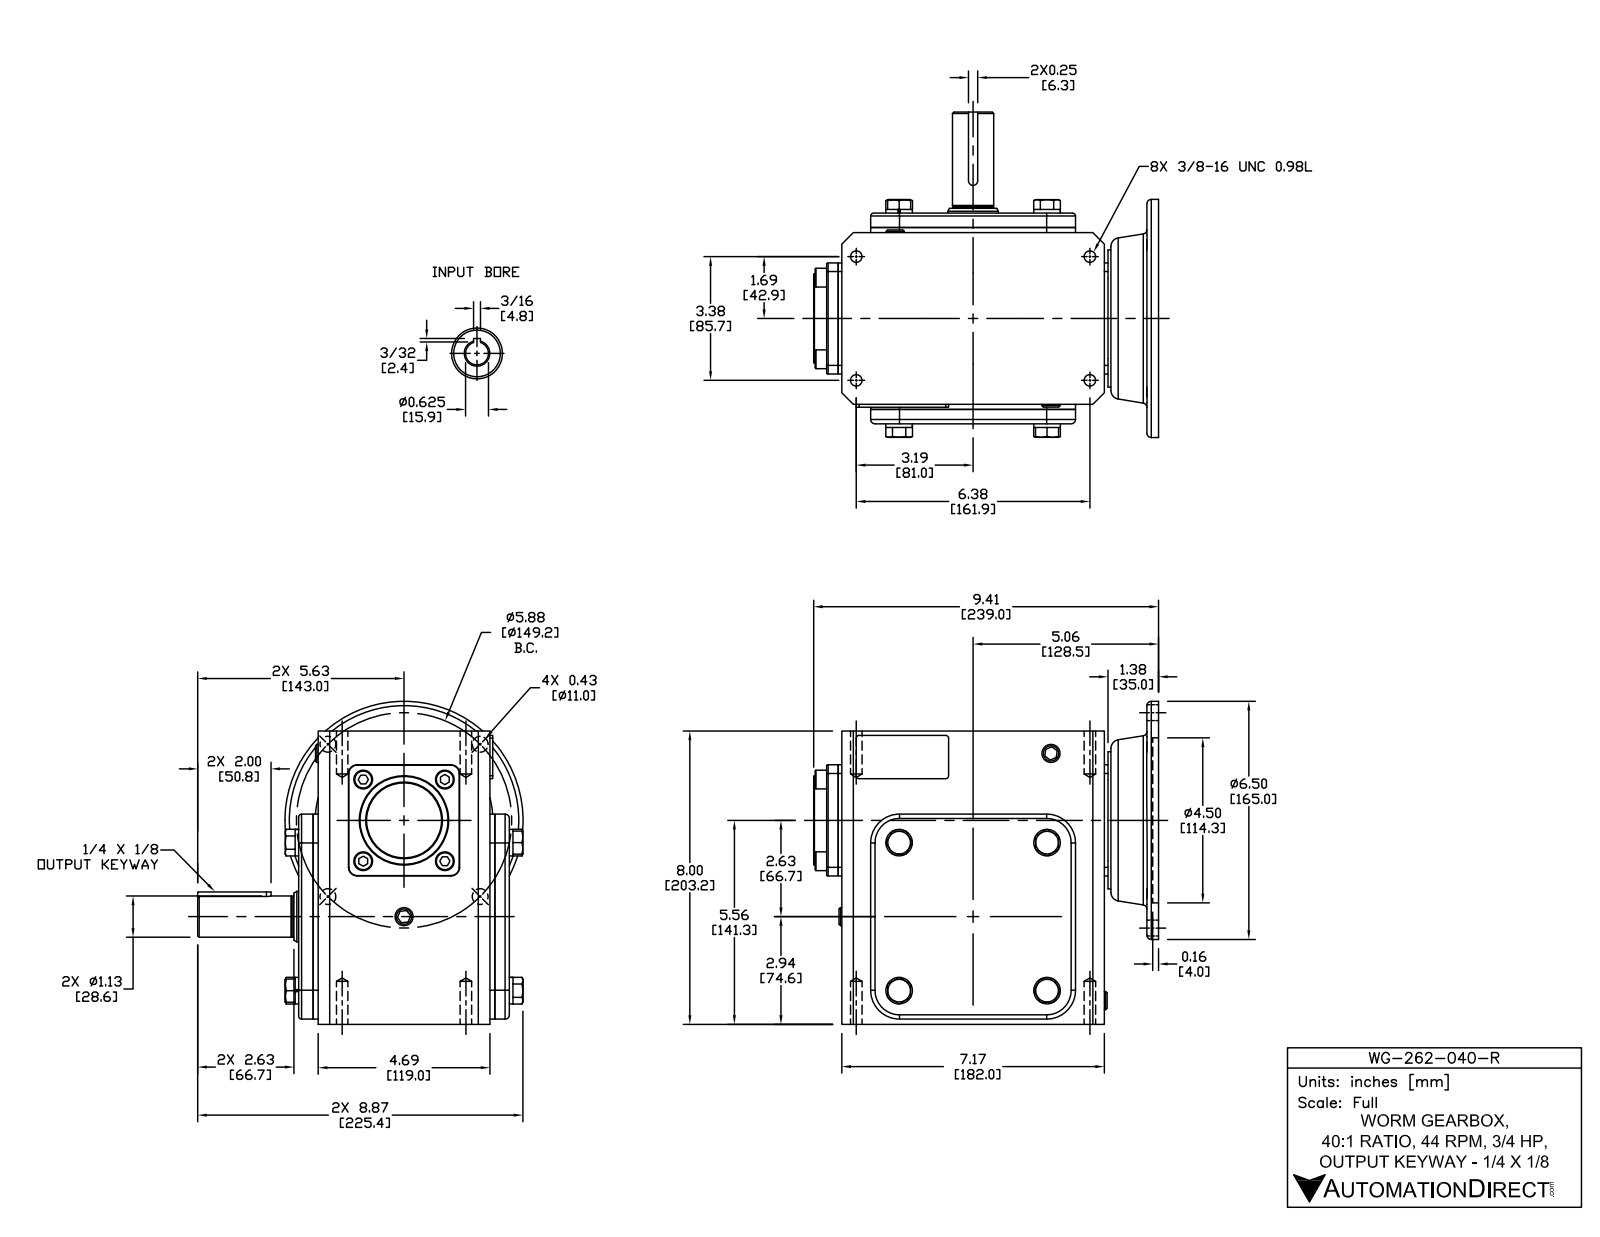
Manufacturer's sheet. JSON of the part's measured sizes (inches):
{"part_name": "WG-262-040-R", "step_written_by": "SolidWorks 2015 (CONFIG_CONTROL_DESIGN)", "units": "inches", "bodies": {"solids": 37, "faces": 527, "planar": 293, "cylindrical": 138, "other": 96}, "overall_size": [9.409, 8.878, 8.811], "volume_in3": 318.1, "surface_area_in2": 613.7, "round_holes": [[0.313, 4], [0.406, 4], [0.591, 1], [0.625, 1], [1.181, 1], [1.378, 1], [1.457, 1], [1.969, 1], [3.819, 1], [4.5, 1]], "round_bosses_or_shafts": [[0.724, 4], [0.512, 4], [6.496, 1], [2.441, 1], [2.047, 1], [1.142, 1], [1.125, 1], [1.113, 1]], "partial_cylinders_radius": [[0.079, 12], [0.118, 4], [0.236, 4], [0.787, 4], [0.02, 2], [0.039, 2], [0.125, 1]], "face_to_face_distances": [0.394, 4.961, 5.354, 5.217, 0.531, 0.138, 4.823, 8, 0.098, 7.264], "hole_center_spacings": [2.937, 4.154, 2.148, 3.375, 5.14, 5.875, 6.375, 7.213]}
